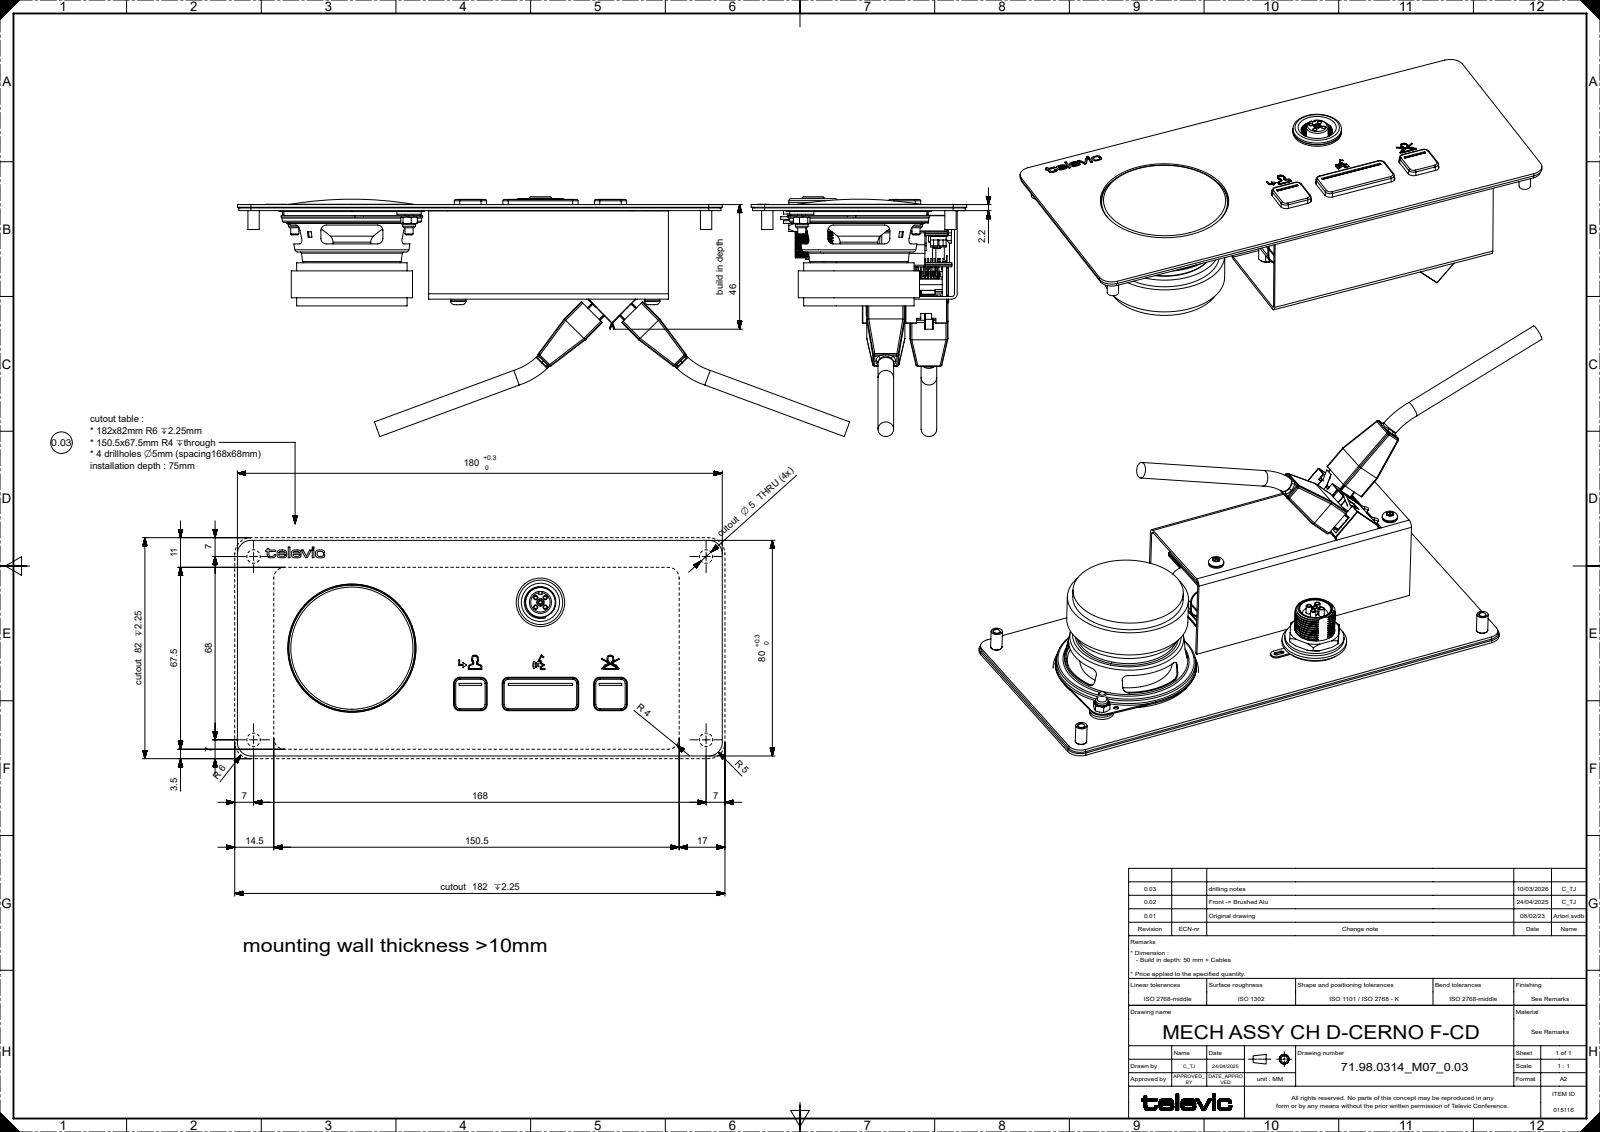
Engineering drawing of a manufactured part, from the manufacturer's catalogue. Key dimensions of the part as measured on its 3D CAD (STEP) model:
Part name (STEP PRODUCT): 3500015_VC-3500015; 3100110_VC-3100110; 3500017_VC-3500017; 310110_VC-310110 (+8 more)
STEP written by: SIEMENS PLM Software NX 2000 (AUTOMOTIVE_DESIGN)
Units: millimetres
Bodies: 98 solids, 4696 faces (2537 planar, 1266 cylindrical, 893 other)
Overall size (bounding box): 245.48 × 88.98 × 80
Volume: 123 070 mm³ · Surface area: 194 560 mm²
Round holes (diameter × count): ⌀2.44 ×6, ⌀2.46 ×6, ⌀3.5 ×6, ⌀4.25 ×6, ⌀1.4 ×5, ⌀3.2 ×5, ⌀3.35 ×4, ⌀1.8 ×2, ⌀4.2 ×2, ⌀6 ×2, ⌀2.8 ×1, ⌀9.7 ×1
Round bosses / shafts (diameter × count): ⌀4.2 ×6, ⌀3.7 ×6, ⌀3 ×6, ⌀2.5 ×6, ⌀2 ×5, ⌀5.8 ×4, ⌀4.6 ×4, ⌀3.3 ×4
Partial cylindrical surfaces — rounded edges, fillets, slot ends (radius × count): R0.25 ×249, R0.5 ×70, R0.2 ×60, R1 ×56, R0.75 ×26, R2 ×23, R2.5 ×16, R1.95 ×12
Main face-to-face distances: 1, 1.25, 11.6, 0.6, 20.5, 1.6, 2.25, 20.85, 22.1, 21.5
Hole centre spacings: 2.5, 3.54, 5.01, 5.38, 28.44, 30, 49.88, 58.2
